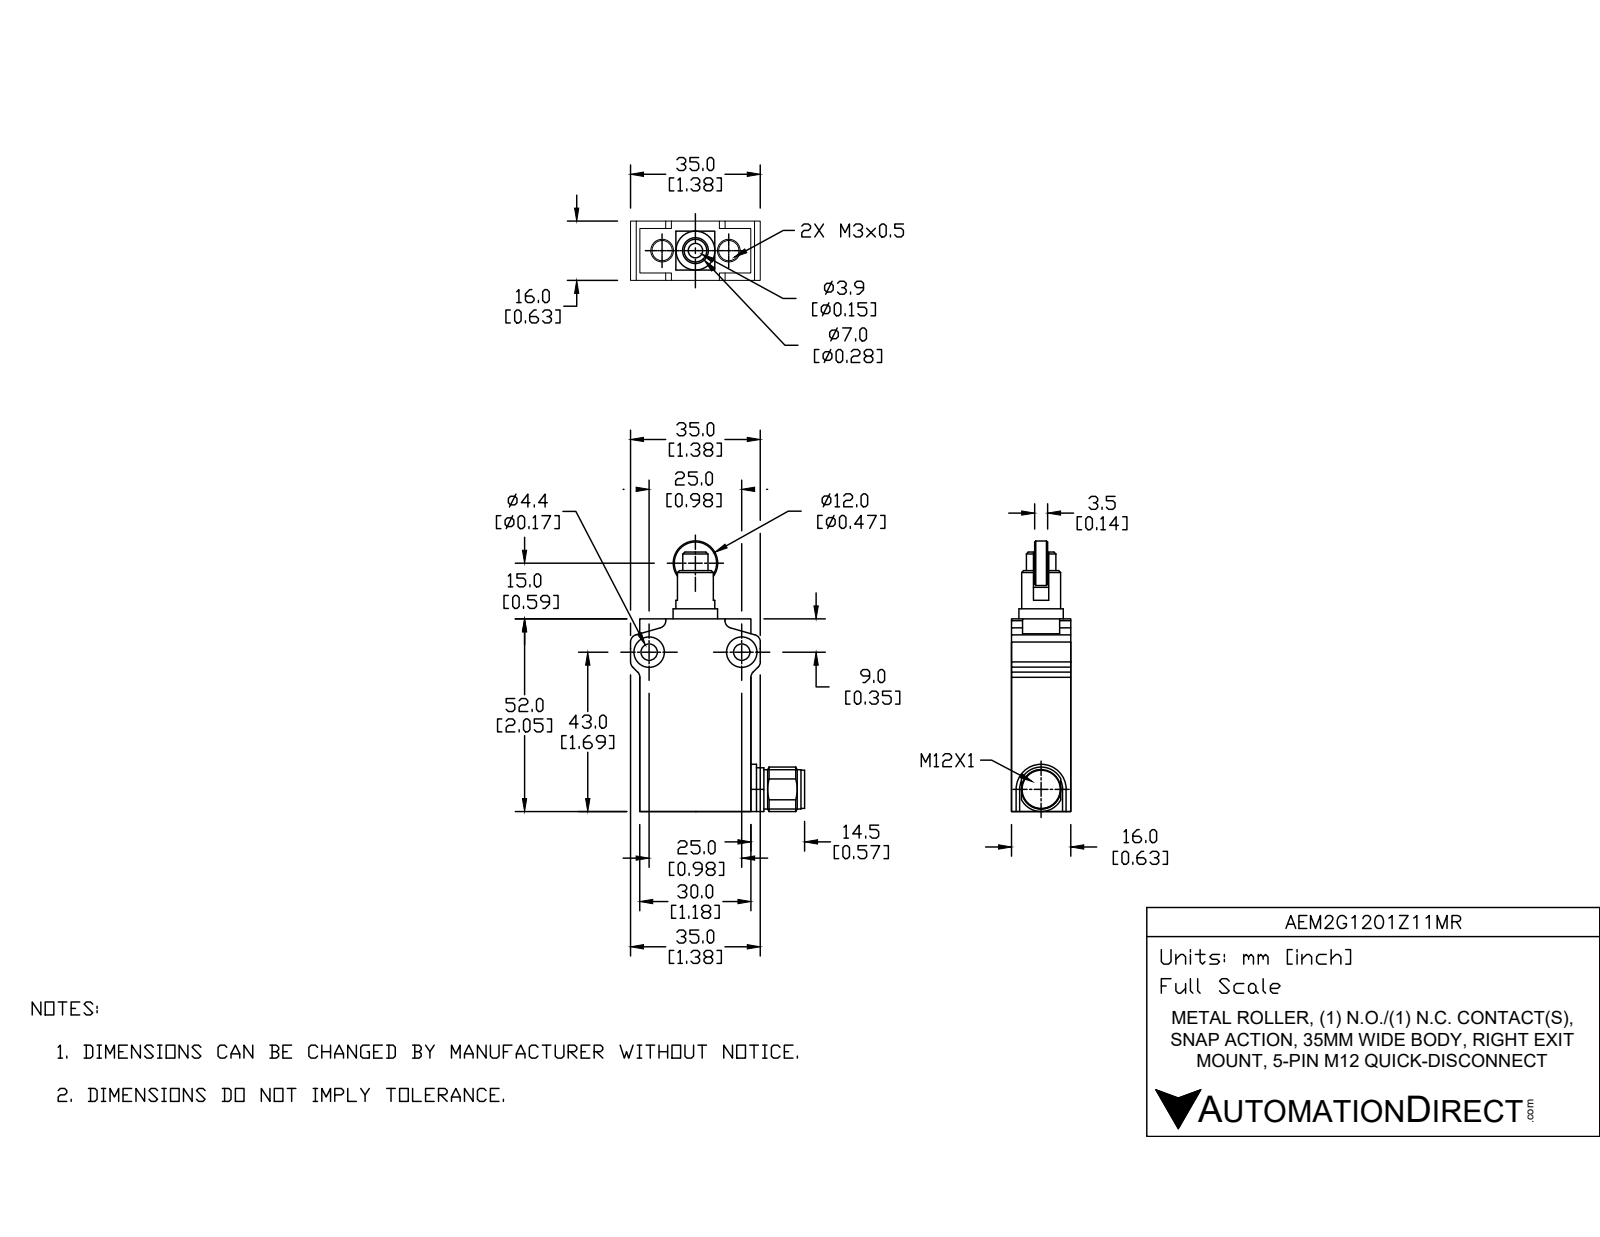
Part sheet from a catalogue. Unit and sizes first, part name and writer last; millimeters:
Units: millimetres
Overall size (bounding box): 73.1 × 46.5 × 16
Round holes (diameter × count): ⌀3 ×2, ⌀4.4 ×2, ⌀8.2 ×2, ⌀8.1 ×1
Round bosses / shafts (diameter × count): ⌀12 ×3, ⌀10.6 ×1, ⌀10.5 ×1, ⌀10.3 ×1, ⌀8 ×1, ⌀5.6 ×1
Partial cylindrical surfaces — rounded edges, fillets, slot ends (radius × count): R2 ×8, R6.5 ×1
Main face-to-face distances: 16, 30, 52, 12, 5.9, 4, 6, 3.8, 10.1, 2.5
Hole centre spacings: 9.5, 19, 25
Volume: 26 940 mm³ · Surface area: 9 619 mm²
Bodies: 5 solids, 157 faces (68 planar, 51 cylindrical, 38 other)
Part name (STEP PRODUCT): AEM2G1201Z11MR
STEP written by: SolidWorks 2019 (AUTOMOTIVE_DESIGN)
